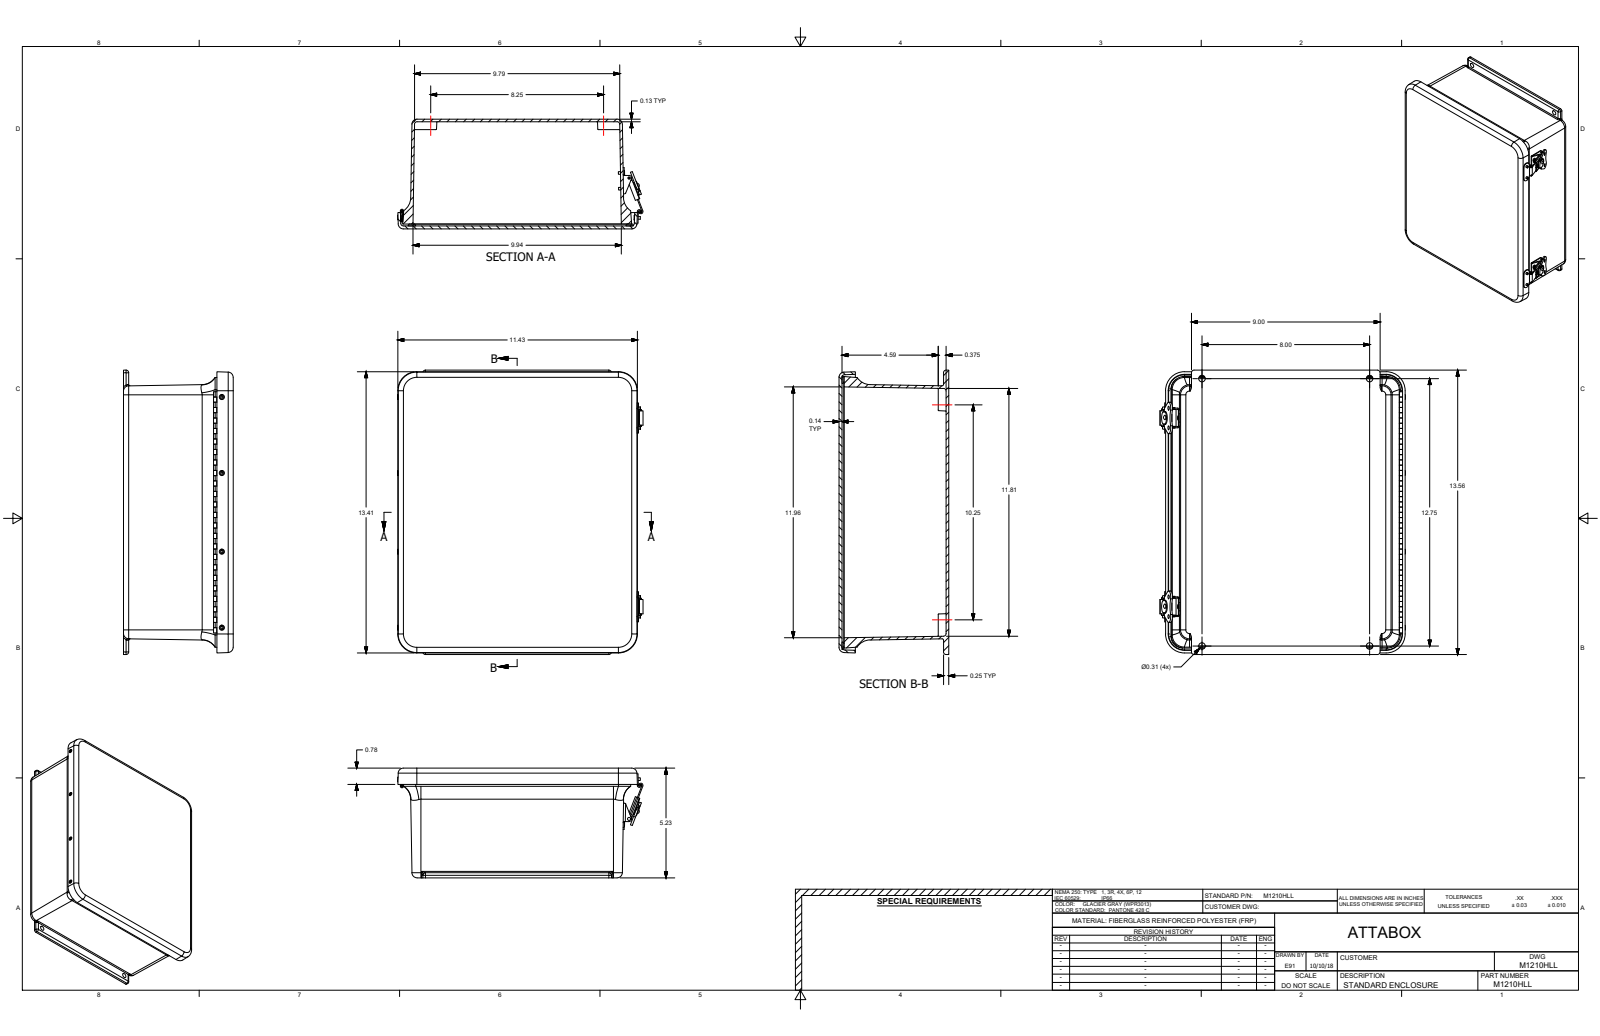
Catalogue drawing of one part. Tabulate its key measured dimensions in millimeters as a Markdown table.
| quantity | value |
| --- | --- |
| part name | M1210HLL |
| STEP written by | SolidWorks 2018 (AUTOMOTIVE_DESIGN) |
| units | millimeters |
| bodies | 46 solids, 1137 faces (480 planar, 469 cylindrical, 188 other) |
| overall size | 344.5 × 297.4 × 133 |
| volume | 1 412 000 mm³ |
| surface area | 772 300 mm² |
| round holes (diameter × count) | 3.6 × 18, 2.6 × 16, 3.3 × 8, 3.9 × 8, 3.3 × 4, 3.4 × 4, 4 × 4, 4.7 × 4, 5.5 × 4, 7.9 × 4, 3.4 × 2, 4.8 × 2 |
| round bosses / shafts (diameter × count) | 3.2 × 12, 3.2 × 6, 6.9 × 4, 16.8 × 2, 14.8 × 2, 13.3 × 2, 7.3 × 2, 5.4 × 2 |
| partial cylindrical surfaces (radius × count) | 0.8 × 36, 3.2 × 17, 0.4 × 16, 1.5 × 13, 6.4 × 10, 0.3 × 8, 0.5 × 8, 1.4 × 8 |
| main face-to-face distances | 3.6, 133, 129.3, 3.2, 129.8, 126.2, 6, 2.3, 123.8, 127 |
| hole center spacings | 228.6, 18.4, 228.6, 3.2, 3.2, 4, 6.4, 28.4 |
